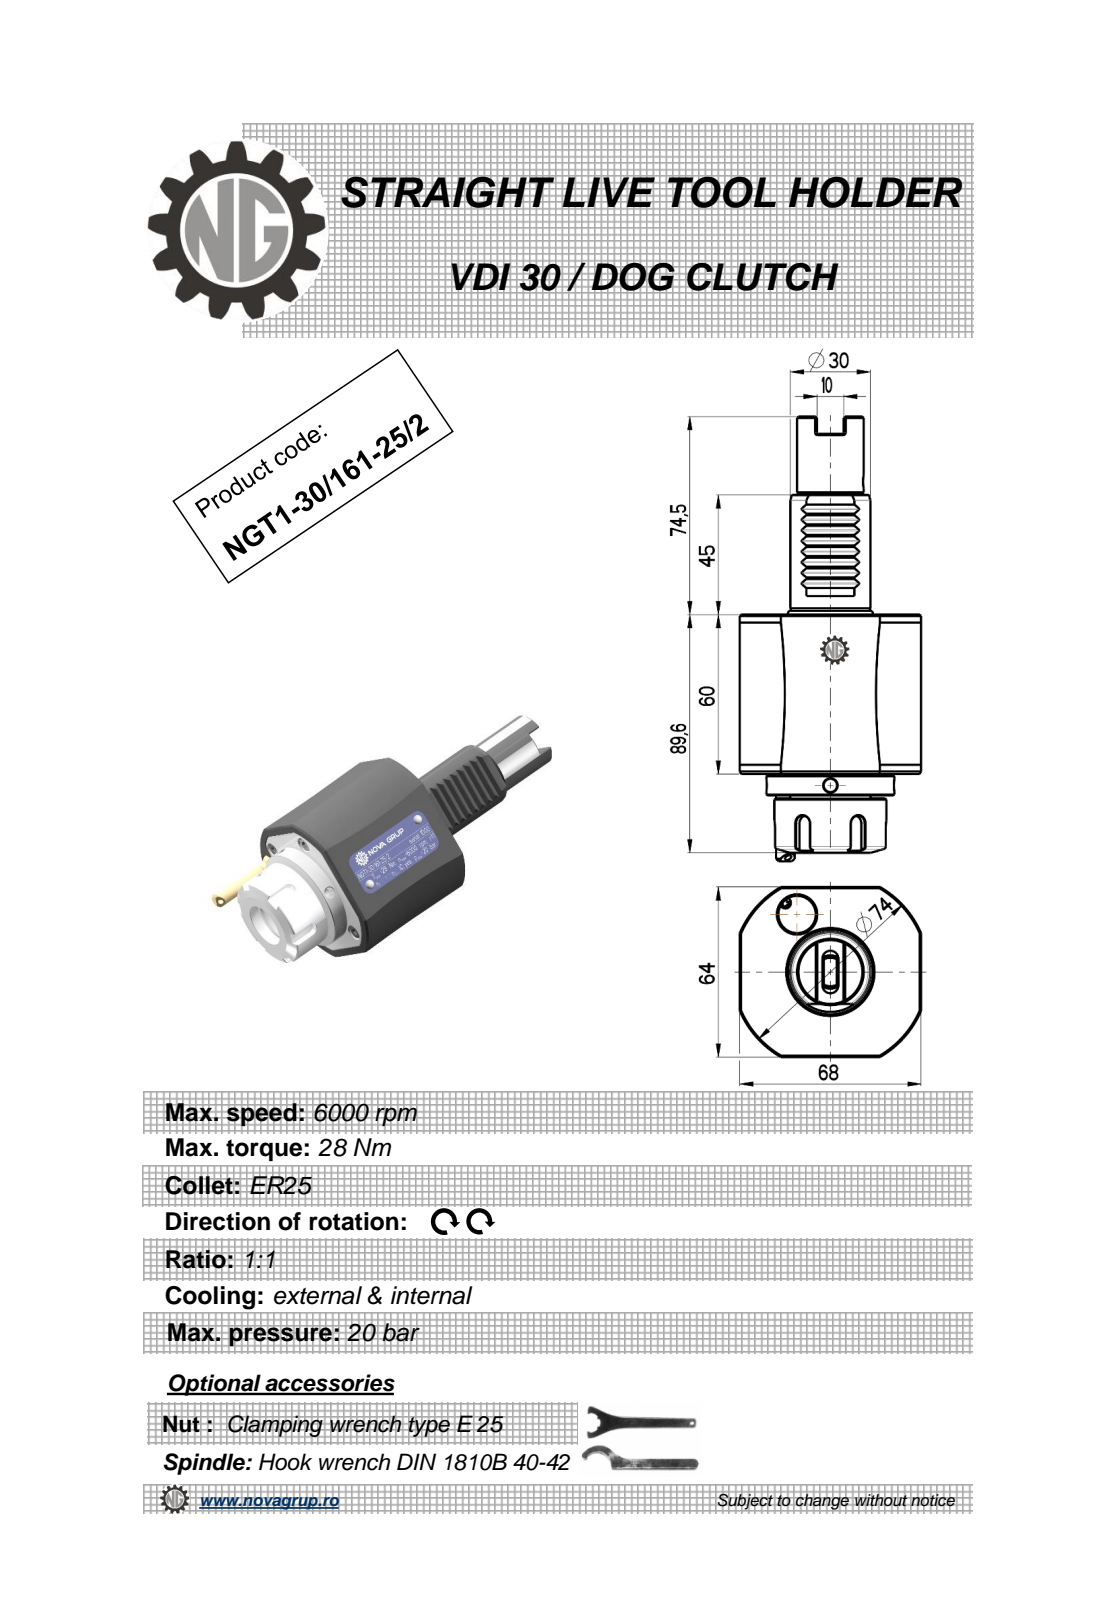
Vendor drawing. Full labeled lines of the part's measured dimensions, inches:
Part name (STEP PRODUCT): NGT1_30_161_25_1
STEP written by: PRO/ENGINEER BY PARAMETRIC TECHNOLOGY CORPORATION, 2010280 (CONFIG_CONTROL_DESIGN)
Units: inches
Bodies: 1 solid, 276 faces (104 planar, 61 cylindrical, 111 other)
Overall size (bounding box): 6.588 × 2.677 × 2.52
Volume: 19.29 in³ · Surface area: 57.7 in²
Round holes (diameter × count): ⌀0.197 ×2, ⌀0.098 ×1, ⌀0.118 ×1, ⌀0.799 ×1
Round bosses / shafts (diameter × count): ⌀1.89 ×1, ⌀1.654 ×1, ⌀1.417 ×1, ⌀1.299 ×1, ⌀1.181 ×1, ⌀0.984 ×1, ⌀0.354 ×1, ⌀0.276 ×1
Partial cylindrical surfaces — rounded edges, fillets, slot ends (radius × count): R0.012 ×8, R0.118 ×5, R0.02 ×2, R1.457 ×1
Main face-to-face distances: 2.362, 2.677, 2.52, 0.315, 0.02, 2.382, 0.295, 4.154, 3.335, 0.972
Hole centre spacings: 1.22
